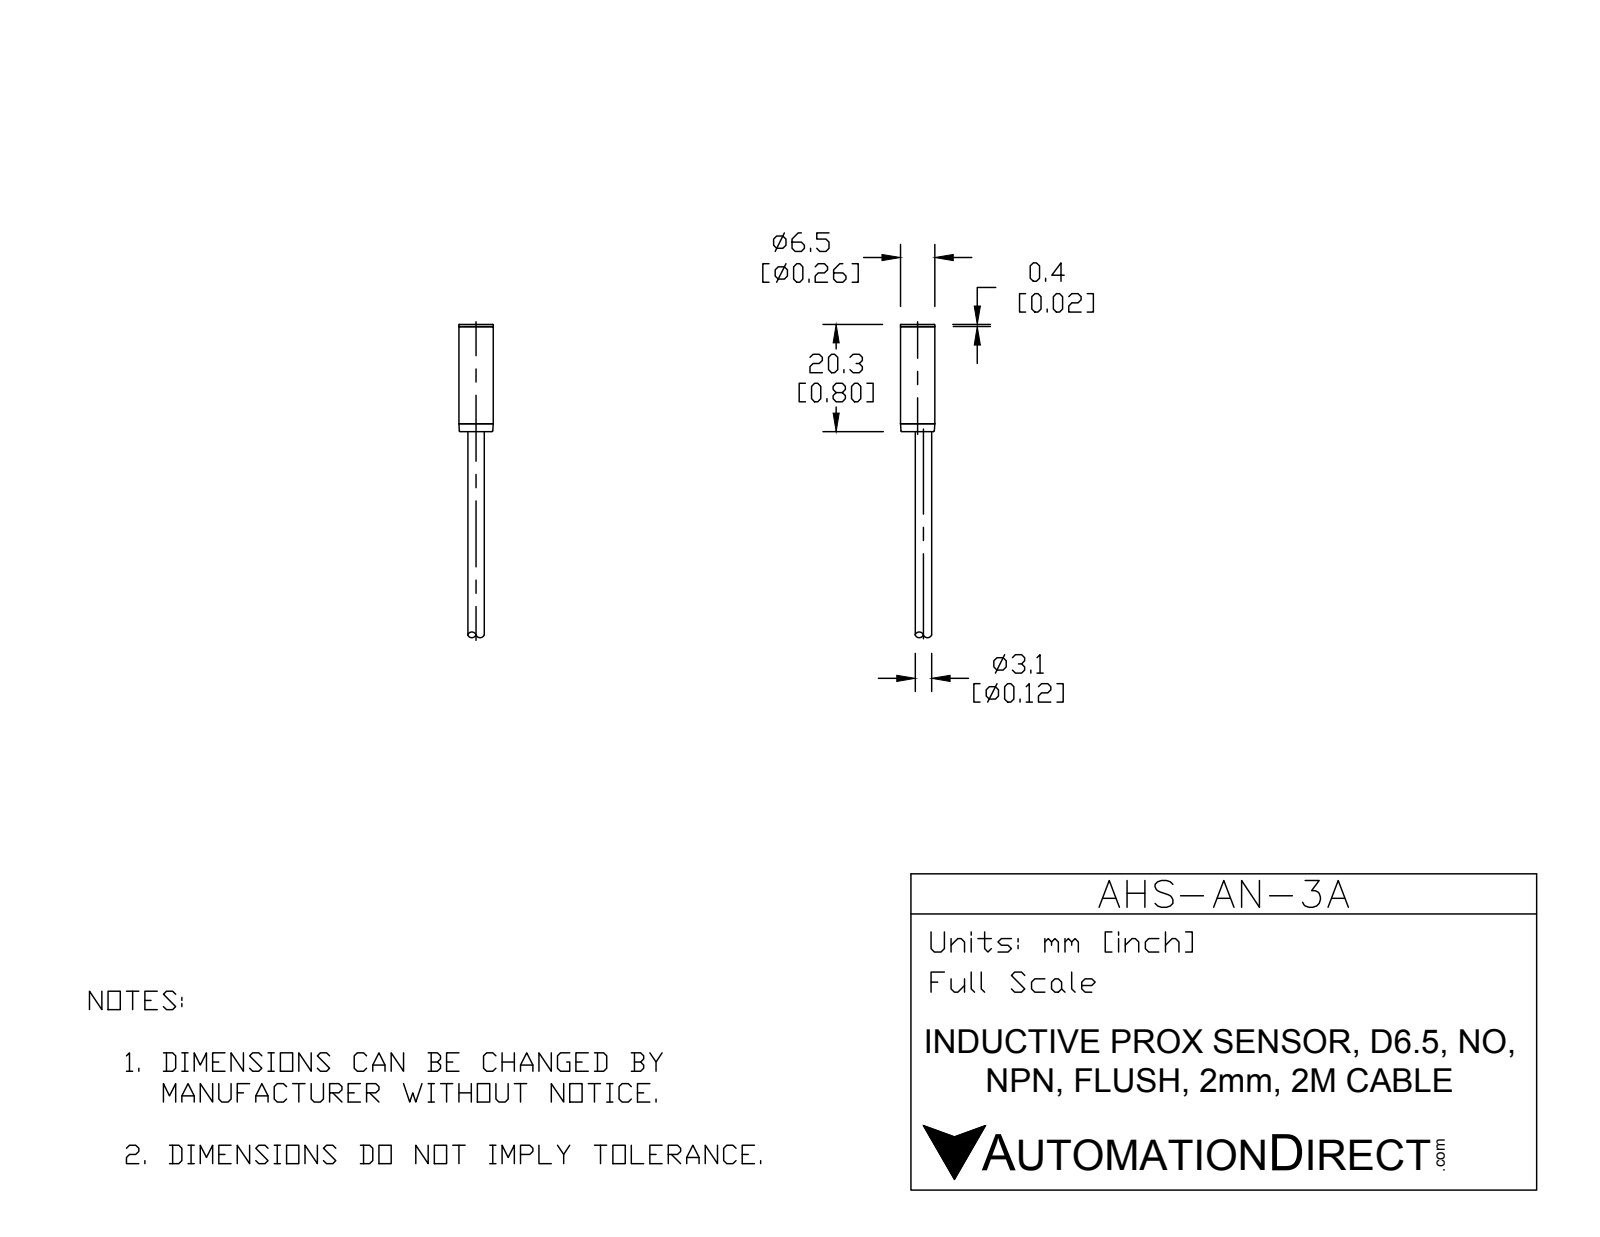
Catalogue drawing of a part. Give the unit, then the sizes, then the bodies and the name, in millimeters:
Units: millimetres
Overall size (bounding box): 70.3 × 6.5 × 6.5
Round bosses / shafts (diameter × count): ⌀6.5 ×1, ⌀3.1 ×1
Main face-to-face distances: 20.3, 50, 70.3, 69.9, 19.9, 0.4
Volume: 1 050 mm³ · Surface area: 979 mm²
Bodies: 2 solids, 17 faces (5 planar, 6 cylindrical, 6 other)
Part name (STEP PRODUCT): AHS-AN-3A
STEP written by: SolidWorks 2015 (CONFIG_CONTROL_DESIGN)
